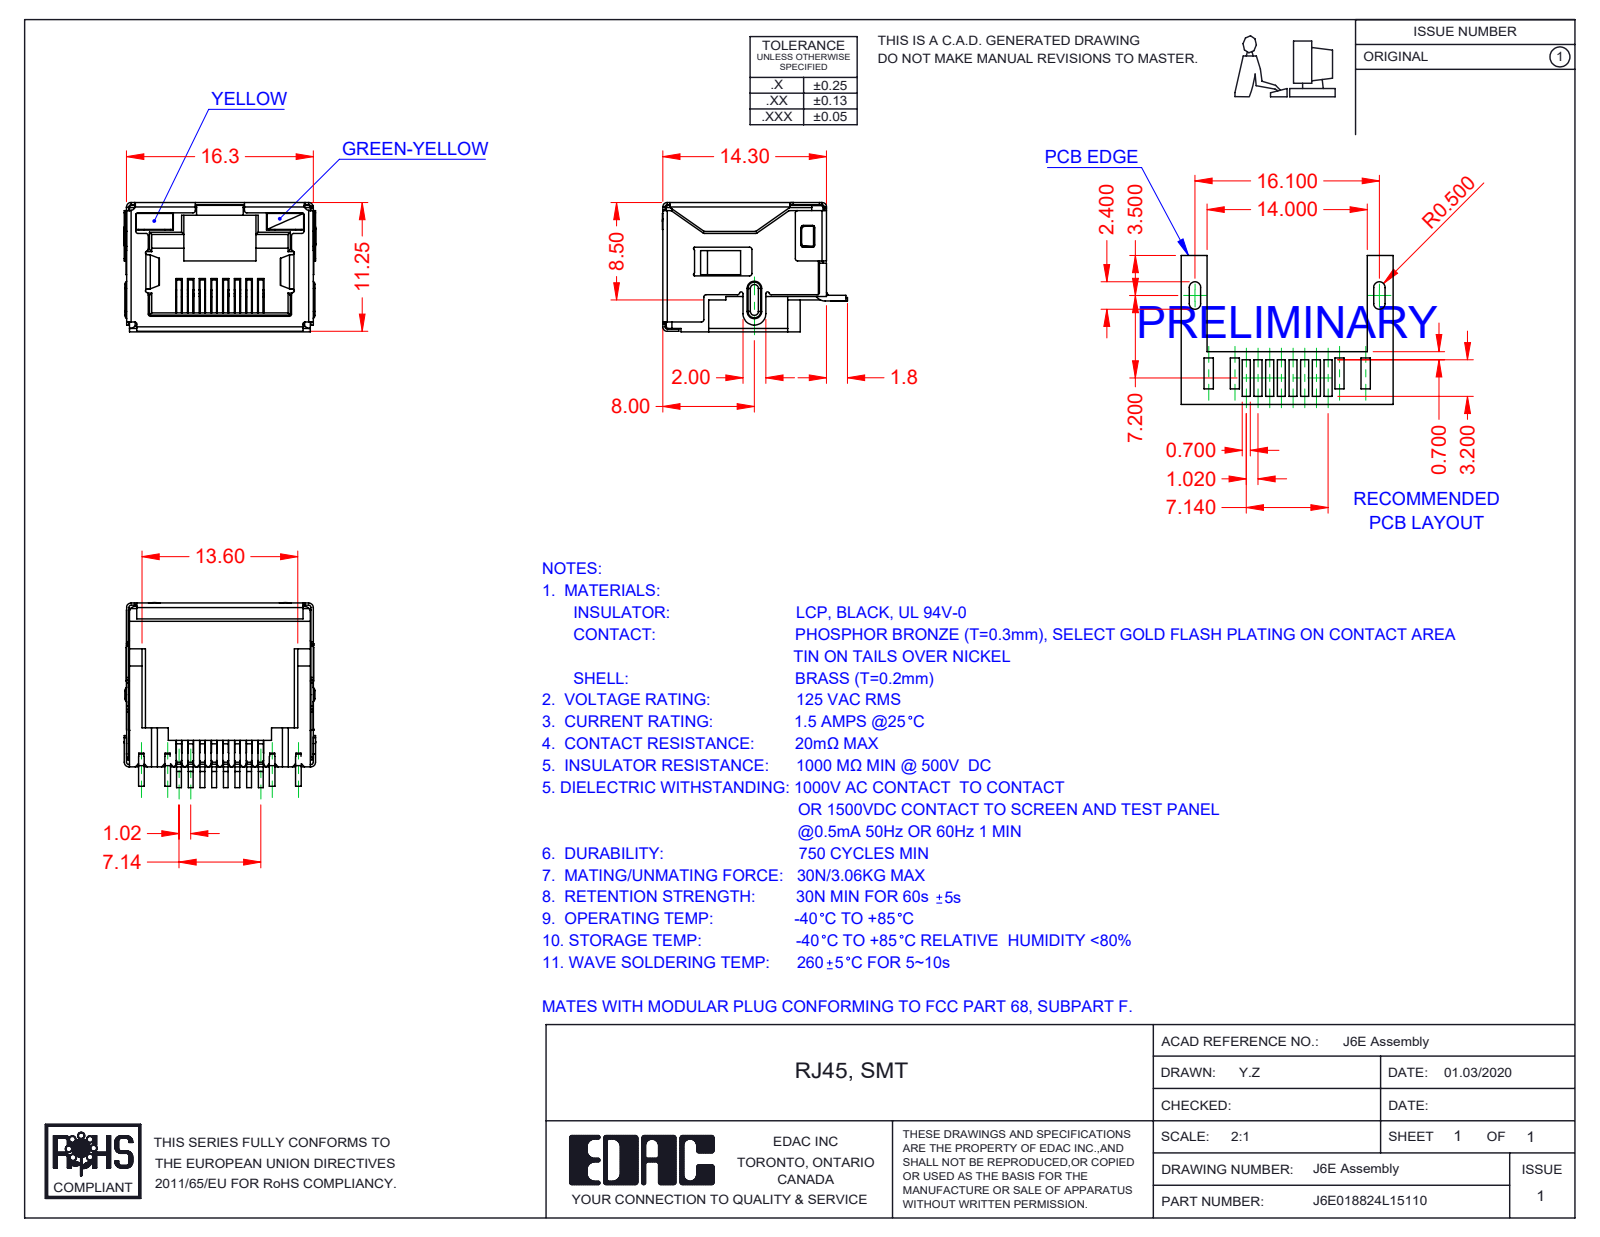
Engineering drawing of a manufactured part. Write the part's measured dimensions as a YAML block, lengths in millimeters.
part_name: "6E Insulator_LED; 6E LED RH_5-Green-Yellow; 6E Contacts; J6E018824L15110 (+2 more)"
step_written_by: "SolidWorks 2016 (CONFIG_CONTROL_DESIGN)"
units: millimeters
bodies: {solids: 12, faces: 1498, planar: 1099, cylindrical: 349, other: 50}
overall_size: [16.75, 16.15, 11.3]
volume: 1109
surface_area: 4045
partial_cylinders:
  - {radius: 0.2, count: 82}
  - {radius: 0.25, count: 17}
  - {radius: 0.4, count: 13}
  - {radius: 0.5, count: 13}
  - {radius: 0.1, count: 10}
  - {radius: 0.15, count: 7}
  - {radius: 0.3, count: 4}
  - {radius: 1, count: 3}
face_to_face_distances: [11.05, 16.05, 16.1, 15.85, 11.1, 11.3, 2.4, 0.7, 9.85, 0.49]
